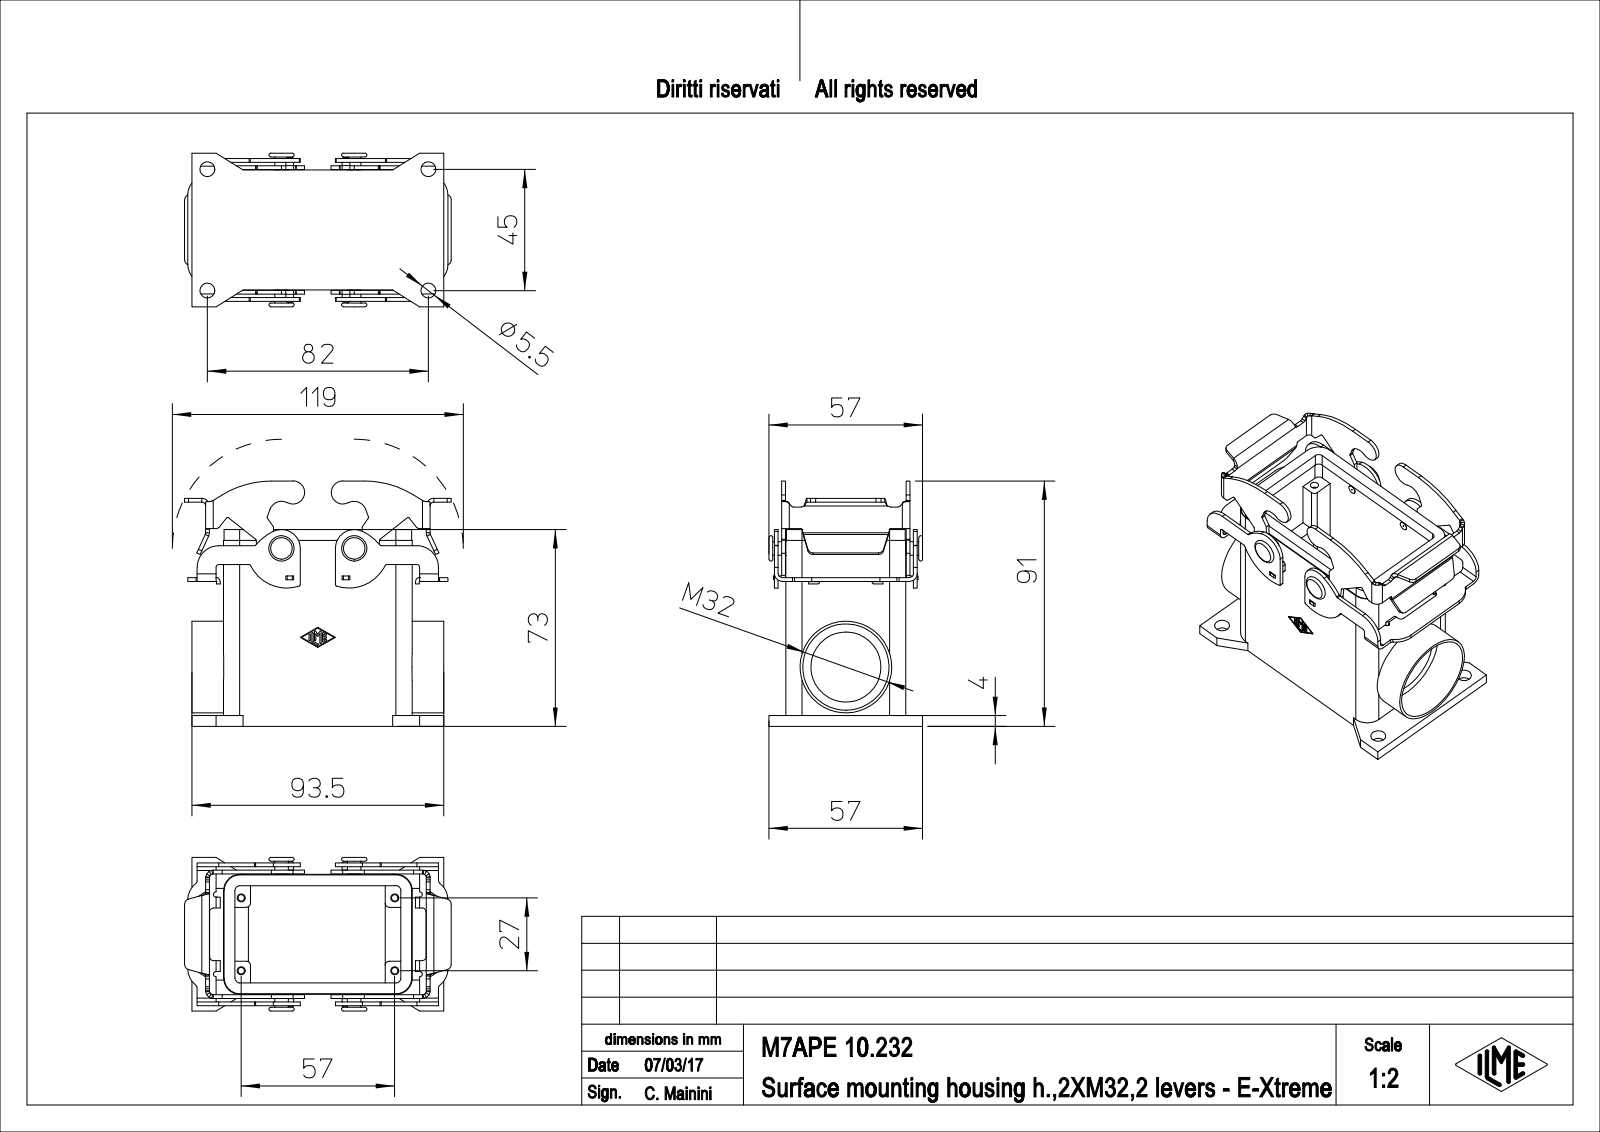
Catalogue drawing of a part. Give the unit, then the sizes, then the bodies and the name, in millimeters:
Units: millimetres
Overall size (bounding box): 98.97 × 91 × 57
Round holes (diameter × count): ⌀2.46 ×4, ⌀3 ×4, ⌀5.5 ×4, ⌀3.5 ×2, ⌀26 ×1, ⌀32 ×1
Round bosses / shafts (diameter × count): ⌀5 ×2, ⌀3.2 ×2, ⌀3 ×2, ⌀34 ×1
Partial cylindrical surfaces — rounded edges, fillets, slot ends (radius × count): R0.5 ×22, R1 ×18, R0.25 ×16, R1.5 ×14, R2 ×12, R1.4 ×10, R2.8 ×10, R8 ×6
Main face-to-face distances: 4, 40.5, 1.4, 44.5, 2.7, 48.9, 36.5, 1.55, 5.55, 42.05
Hole centre spacings: 15.4, 38.11, 70.08, 78.27, 27, 45, 57, 63.07
Volume: 95 703 mm³ · Surface area: 59 848 mm²
Bodies: 1 solid, 613 faces (295 planar, 272 cylindrical, 46 other)
Part name (STEP PRODUCT): M7APE_10.232
STEP written by: PTC Creo Elements/Direct Modeling 19.0E 27-Jun-2016 (C) Parametric Technology GmbH (AUTOMOTIVE_DESIGN)
